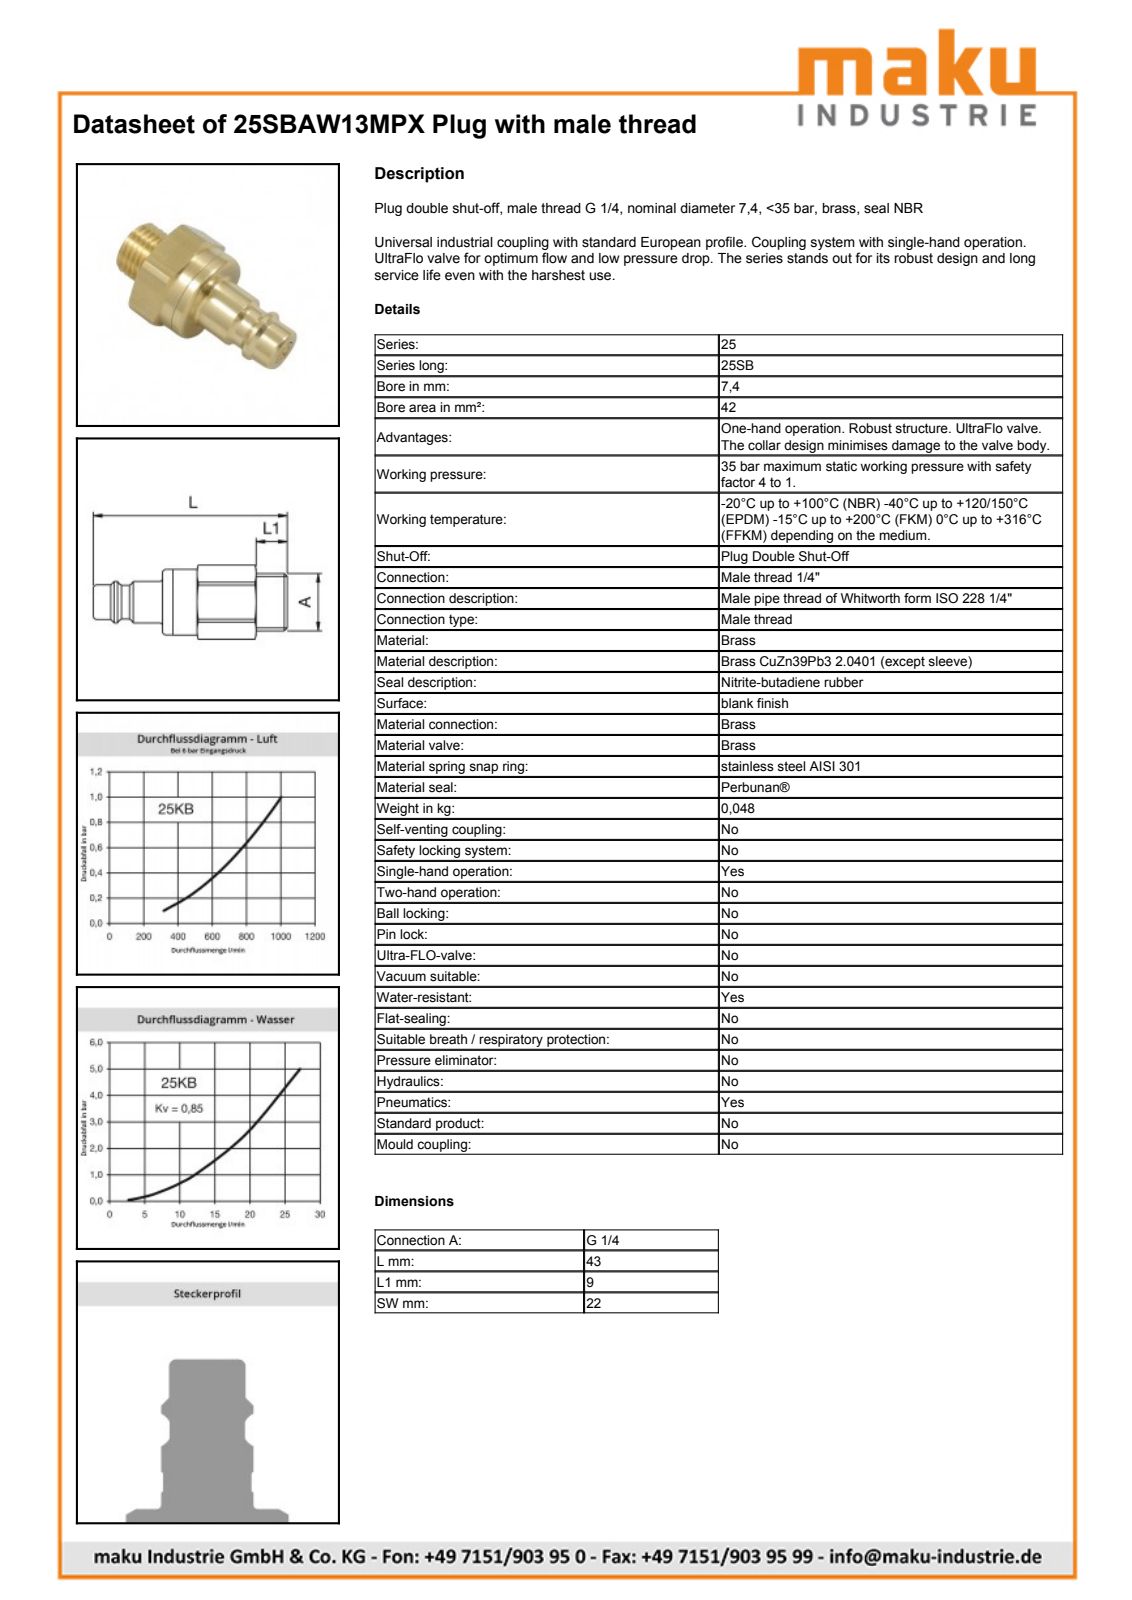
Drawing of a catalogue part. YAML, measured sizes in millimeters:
part_name: "D105309"
step_written_by: "Autodesk Inventor 2011 (AUTOMOTIVE_DESIGN)"
units: millimeters
bodies: {solids: 1, faces: 45, planar: 12, cylindrical: 13, other: 20}
overall_size: [46.6, 24.8, 22.67]
volume: 9185
surface_area: 3035
round_bosses_or_shafts:
  - {diameter: 21, count: 1}
  - {diameter: 17.47, count: 1}
  - {diameter: 13.16, count: 1}
  - {diameter: 12, count: 1}
  - {diameter: 10, count: 1}
  - {diameter: 9.75, count: 1}
partial_cylinders:
  - {radius: 12.4, count: 1}
face_to_face_distances: [22, 14.6, 26.6, 12, 20, 34.6, 46.6, 26.1, 6.1, 8.5]
